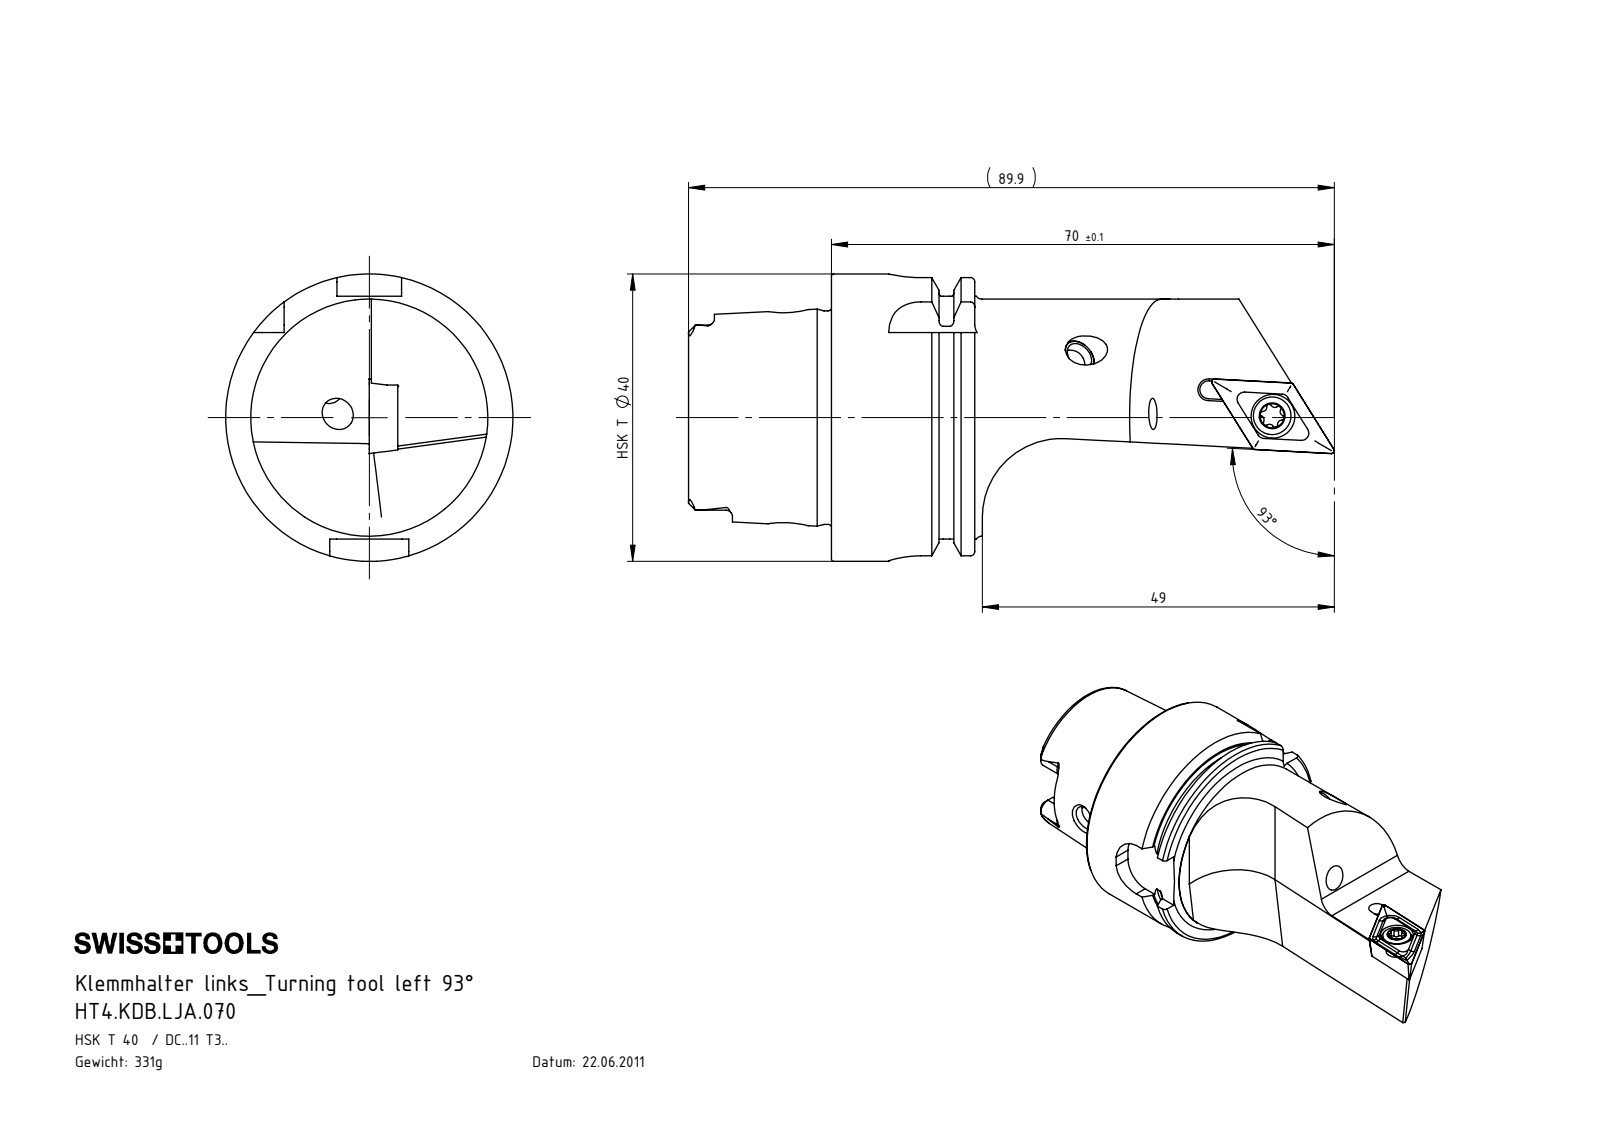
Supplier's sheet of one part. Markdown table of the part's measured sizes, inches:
| quantity | value |
| --- | --- |
| part name | KVT_MB_600_050; HA4-KDB.LJA.070_B_Fertigbearbeitung; HT4.KDB.LJA.070; DCMT11T304 (+1 more) |
| STEP written by | SolidWorks 2022 (CONFIG_CONTROL_DESIGN) |
| units | inches |
| bodies | 5 solids, 307 faces (79 planar, 87 cylindrical, 141 other) |
| overall size | 3.54 × 1.575 × 1.575 |
| volume | 2.559 in³ |
| surface area | 21.99 in² |
| round holes (diameter × count) | 0.157 × 2, 0.165 × 2, 0.13 × 1, 0.173 × 1, 0.181 × 1, 0.197 × 1, 0.24 × 1, 0.394 × 1, 0.433 × 1, 0.492 × 1, 0.827 × 1, 1.004 × 1 |
| round bosses / shafts (diameter × count) | 1.575 × 1, 1.368 × 1, 1.299 × 1, 1.17 × 1, 0.207 × 1, 0.197 × 1, 0.157 × 1 |
| partial cylindrical surfaces (radius × count) | 0.013 × 6, 0.023 × 6, 0.035 × 6, 0.074 × 4, 0.177 × 4, 0.049 × 1, 0.118 × 1, 0.433 × 1 |
| main face-to-face distances | 0.313, 0.785, 0.472, 0.144, 0.783, 1.096, 1.569, 1.406, 0.622, 0.309 |
| hole center spacings | 2.14, 2.144 |
